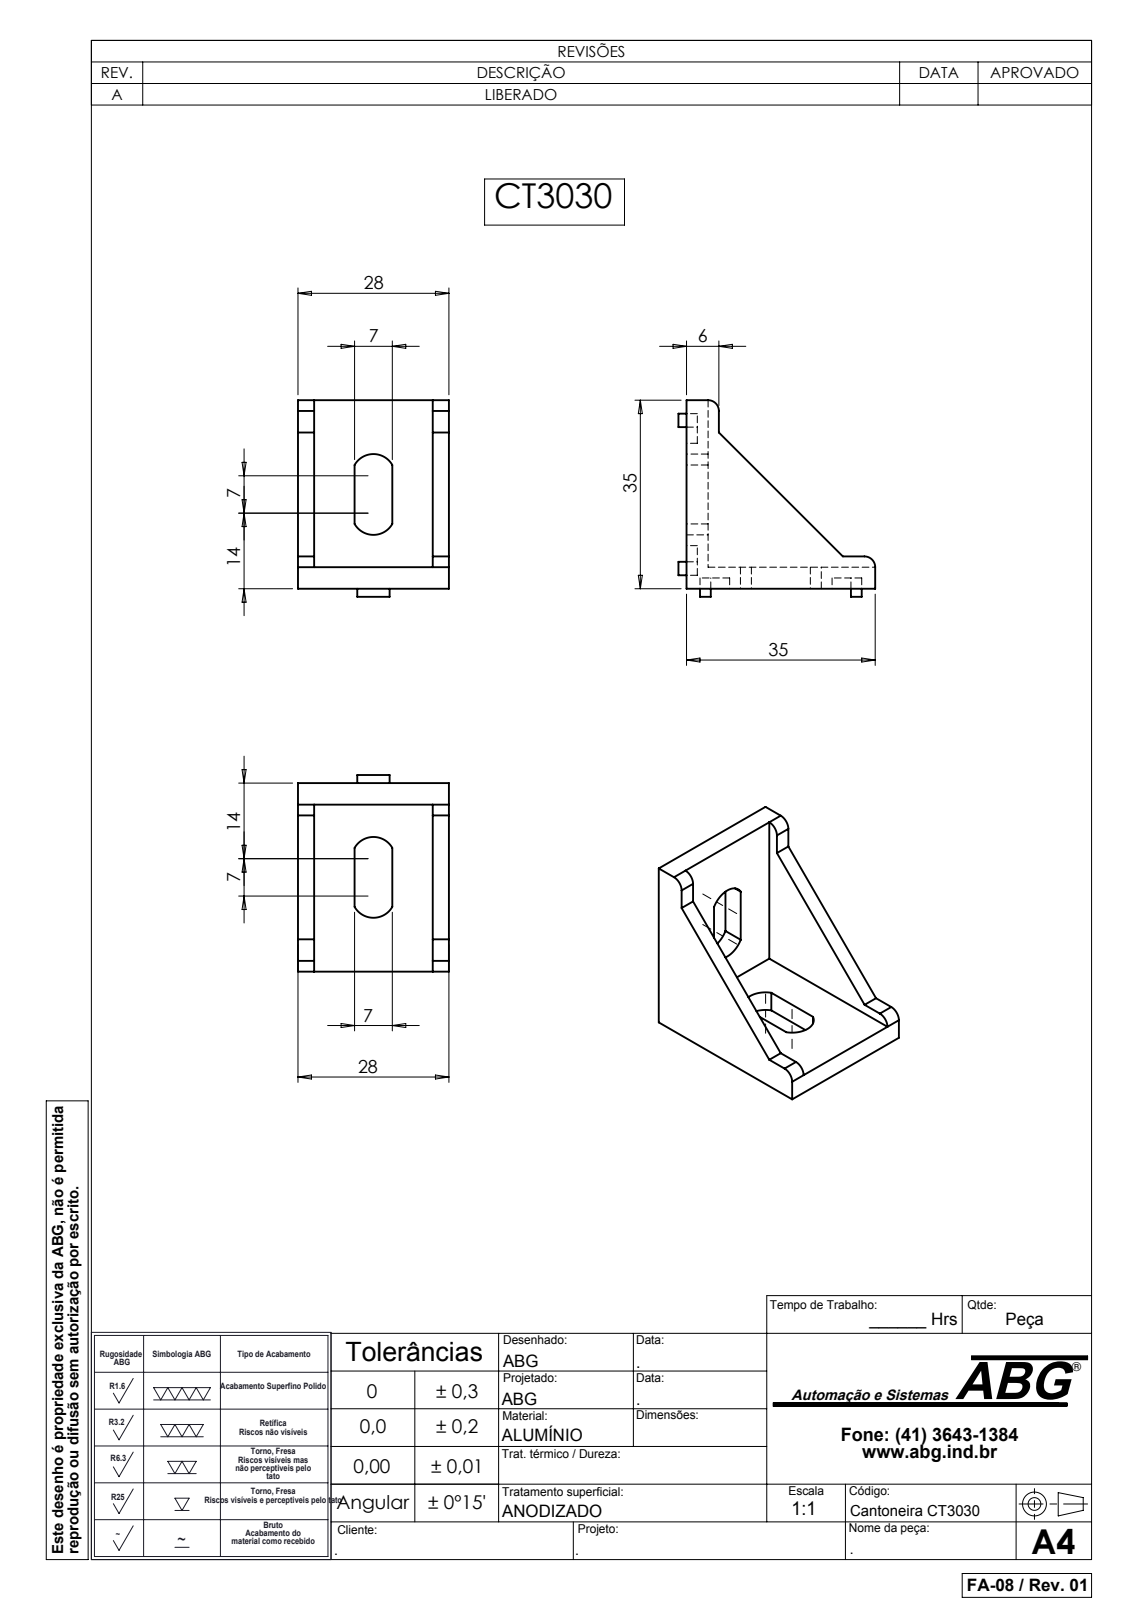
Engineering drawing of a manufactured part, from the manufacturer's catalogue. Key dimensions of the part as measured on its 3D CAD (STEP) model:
Part name (STEP PRODUCT): CT3030
STEP written by: SolidWorks 2007 (CONFIG_CONTROL_DESIGN)
Units: millimetres
Bodies: 1 solid, 73 faces (64 planar, 9 cylindrical, 0 other)
Overall size (bounding box): 36.5 × 36.5 × 28
Volume: 8 554 mm³ · Surface area: 6 235 mm²
Partial cylindrical surfaces — rounded edges, fillets, slot ends (radius × count): R4.03 ×4, R2 ×2
Main face-to-face distances: 4, 25, 3, 28, 2, 22, 35, 31, 7.5, 33
